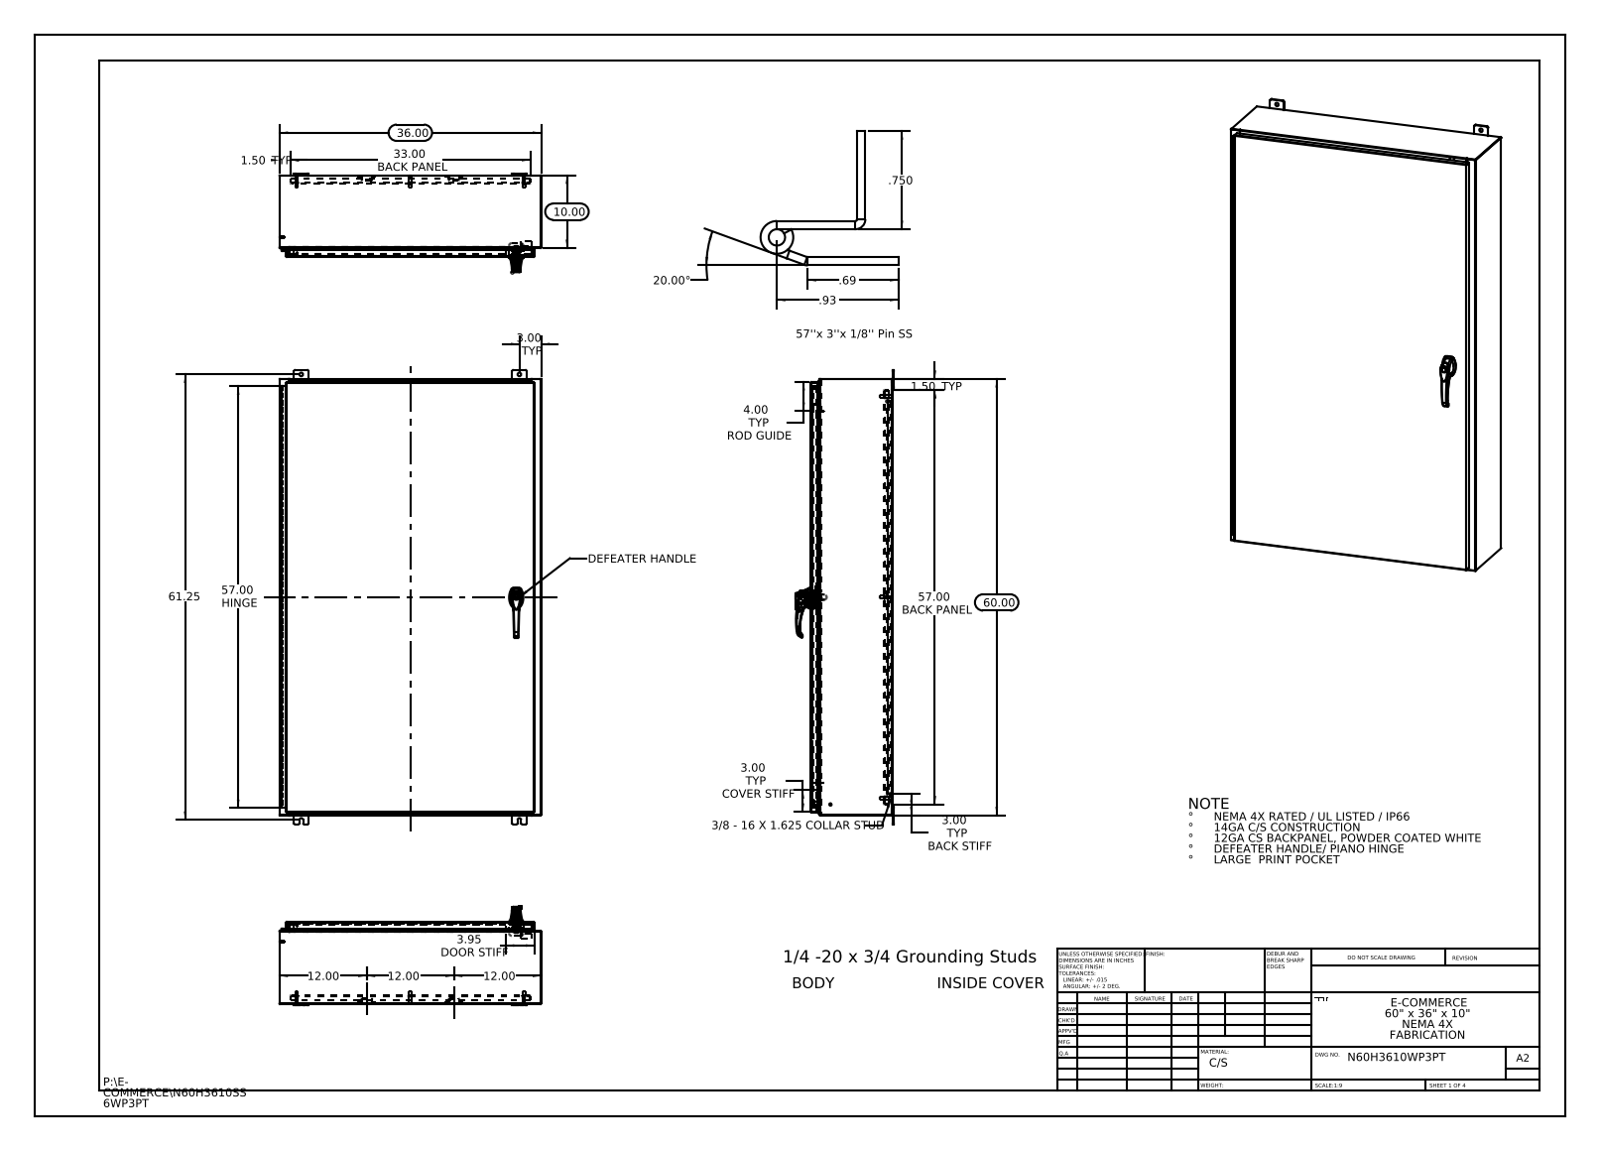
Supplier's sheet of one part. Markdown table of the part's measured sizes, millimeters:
| quantity | value |
| --- | --- |
| part name | 21130102; 297026; N60H3610SS6WP3PT Body; 012103_012102 (+8 more) |
| STEP written by | SolidWorks 2013 (CONFIG_CONTROL_DESIGN) |
| units | millimeters |
| bodies | 51 solids, 3712 faces (1465 planar, 1461 cylindrical, 786 other) |
| overall size | 1612.9 × 914.4 × 342.8 |
| volume | 12 800 000 mm³ |
| surface area | 12 480 000 mm² |
| round holes (diameter × count) | 12.7 × 12, 6.4 × 10, 3.5 × 3, 4.1 × 3, 2 × 2, 5.2 × 2, 8 × 2, 11.1 × 2, 3.2 × 1, 3.2 × 1, 5 × 1, 7 × 1 |
| round bosses / shafts (diameter × count) | 4 × 10, 3.6 × 10, 15.9 × 8, 9.5 × 8, 8.4 × 8, 8 × 3, 6 × 3, 30 × 1 |
| partial cylindrical surfaces (radius × count) | 3 × 37, 0.3 × 34, 0.2 × 33, 2.2 × 28, 4.8 × 24, 1 × 15, 0.7 × 12, 0.2 × 6 |
| main face-to-face distances | 1.9, 282.6, 280.7, 2.6, 284.5, 25.4, 257.2, 27.3, 255.3, 29.9 |
| hole center spacings | 605.9, 664.5, 714.4, 817.2, 1067.9, 1482.9, 793.8, 1428.8 |
